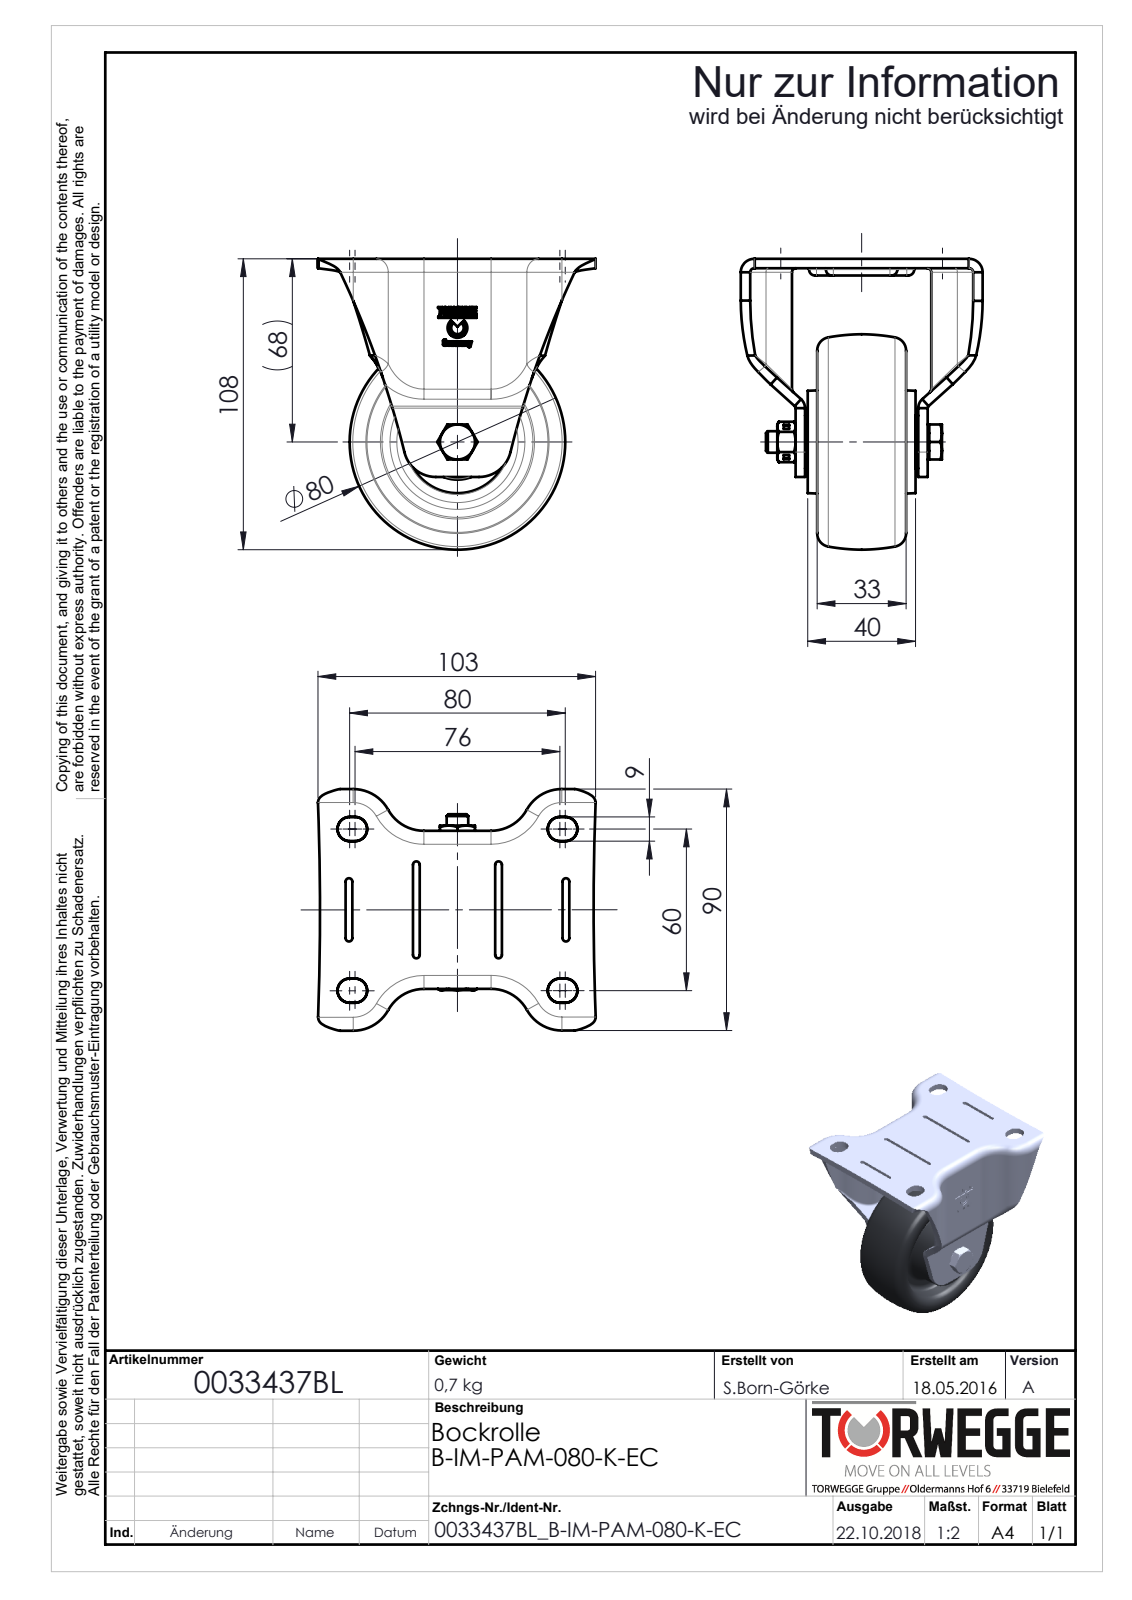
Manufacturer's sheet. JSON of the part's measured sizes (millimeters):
{"part_name": "0033437BL_B-IM-PAM-080-K-EC", "step_written_by": "SolidWorks 2016 (AUTOMOTIVE_DESIGN)", "units": "millimeters", "bodies": {"solids": 0, "faces": 745, "planar": 337, "cylindrical": 226, "other": 182}, "overall_size": [108, 103.04, 89.74], "round_holes": [[6.8, 1], [8, 1], [8.2, 1], [12, 1], [12.4, 1], [16.8, 1], [23, 1], [23.2, 1]], "round_bosses_or_shafts": [[28, 1], [20, 1], [15, 1], [13, 1], [11.9, 1]], "partial_cylinders_radius": [[4.5, 10], [5, 9], [0.27, 8], [1.25, 8], [2.2, 8], [2.75, 8], [0.15, 7], [0.45, 7]], "face_to_face_distances": [3.5, 45.5, 4.85, 50.35, 4.5, 44.5, 1, 41, 32, 42]}
